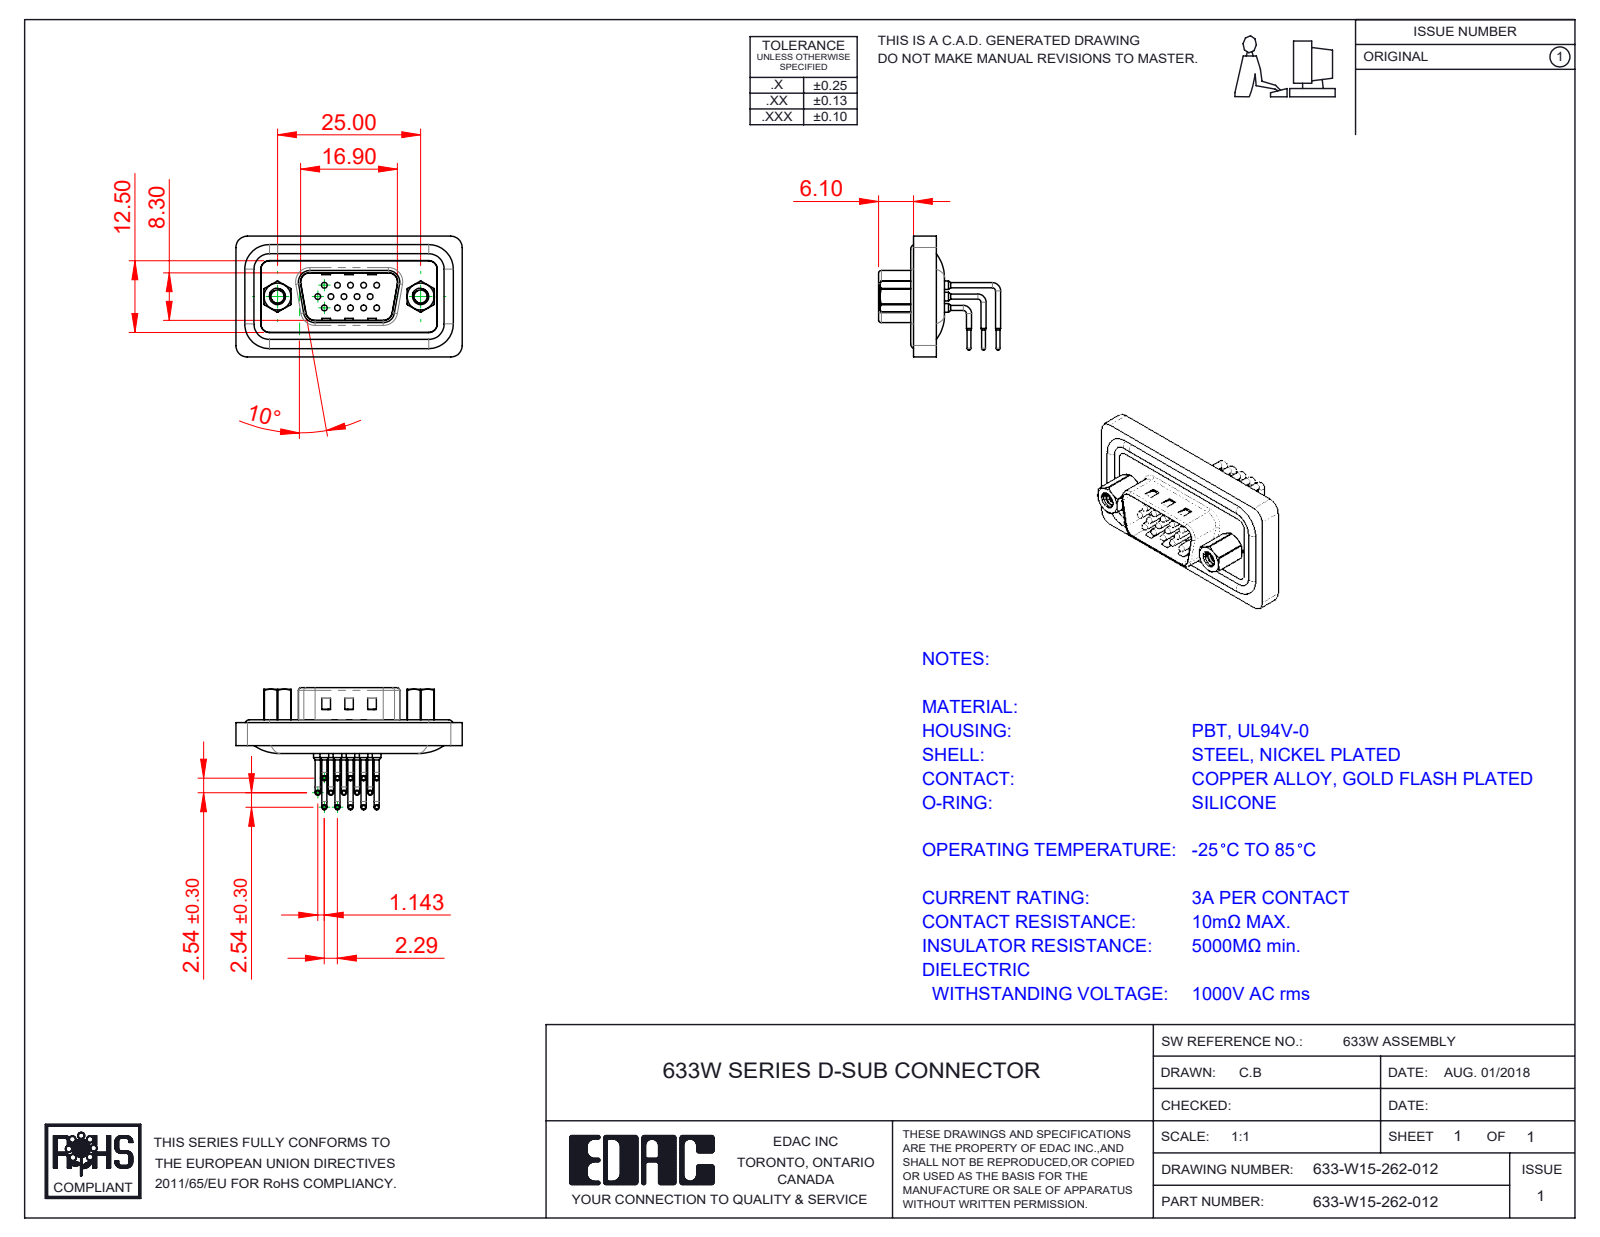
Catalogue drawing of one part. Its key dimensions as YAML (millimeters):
part_name: "633-W15-262-012; 633W Waterproof Housing_15 Contacts; 633W Shell_15 Contacts; 633W Contact Row 2 (+5 more)"
step_written_by: "SolidWorks 2023 (CONFIG_CONTROL_DESIGN)"
units: millimeters
bodies: {solids: 23, faces: 2120, planar: 1101, cylindrical: 776, other: 243}
overall_size: [39.51, 21.52, 21.1]
volume: 4066
surface_area: 7300
round_holes:
  - {diameter: 1, count: 15}
  - {diameter: 1.5, count: 15}
  - {diameter: 1.7, count: 15}
  - {diameter: 2, count: 15}
  - {diameter: 2.26, count: 2}
  - {diameter: 2.29, count: 2}
  - {diameter: 4, count: 2}
  - {diameter: 4.8, count: 2}
  - {diameter: 5, count: 2}
round_bosses_or_shafts:
  - {diameter: 0.9, count: 30}
  - {diameter: 0.65, count: 15}
  - {diameter: 1.5, count: 8}
  - {diameter: 1.6, count: 4}
  - {diameter: 4.9, count: 2}
  - {diameter: 2.79, count: 2}
  - {diameter: 5, count: 1}
partial_cylinders:
  - {radius: 1.01, count: 15}
  - {radius: 1.5, count: 14}
  - {radius: 2, count: 14}
  - {radius: 0.5, count: 8}
  - {radius: 2.7, count: 6}
  - {radius: 0.9, count: 4}
  - {radius: 1.6, count: 4}
  - {radius: 4.3, count: 4}
face_to_face_distances: [0.4, 1.6, 2.9, 1.1, 2.5, 4, 3.6, 1.8, 0.7, 0.5]
hole_center_spacings: [3.96, 2.28, 4.57, 2.29, 6.05, 6.04, 7.92, 6.86]
